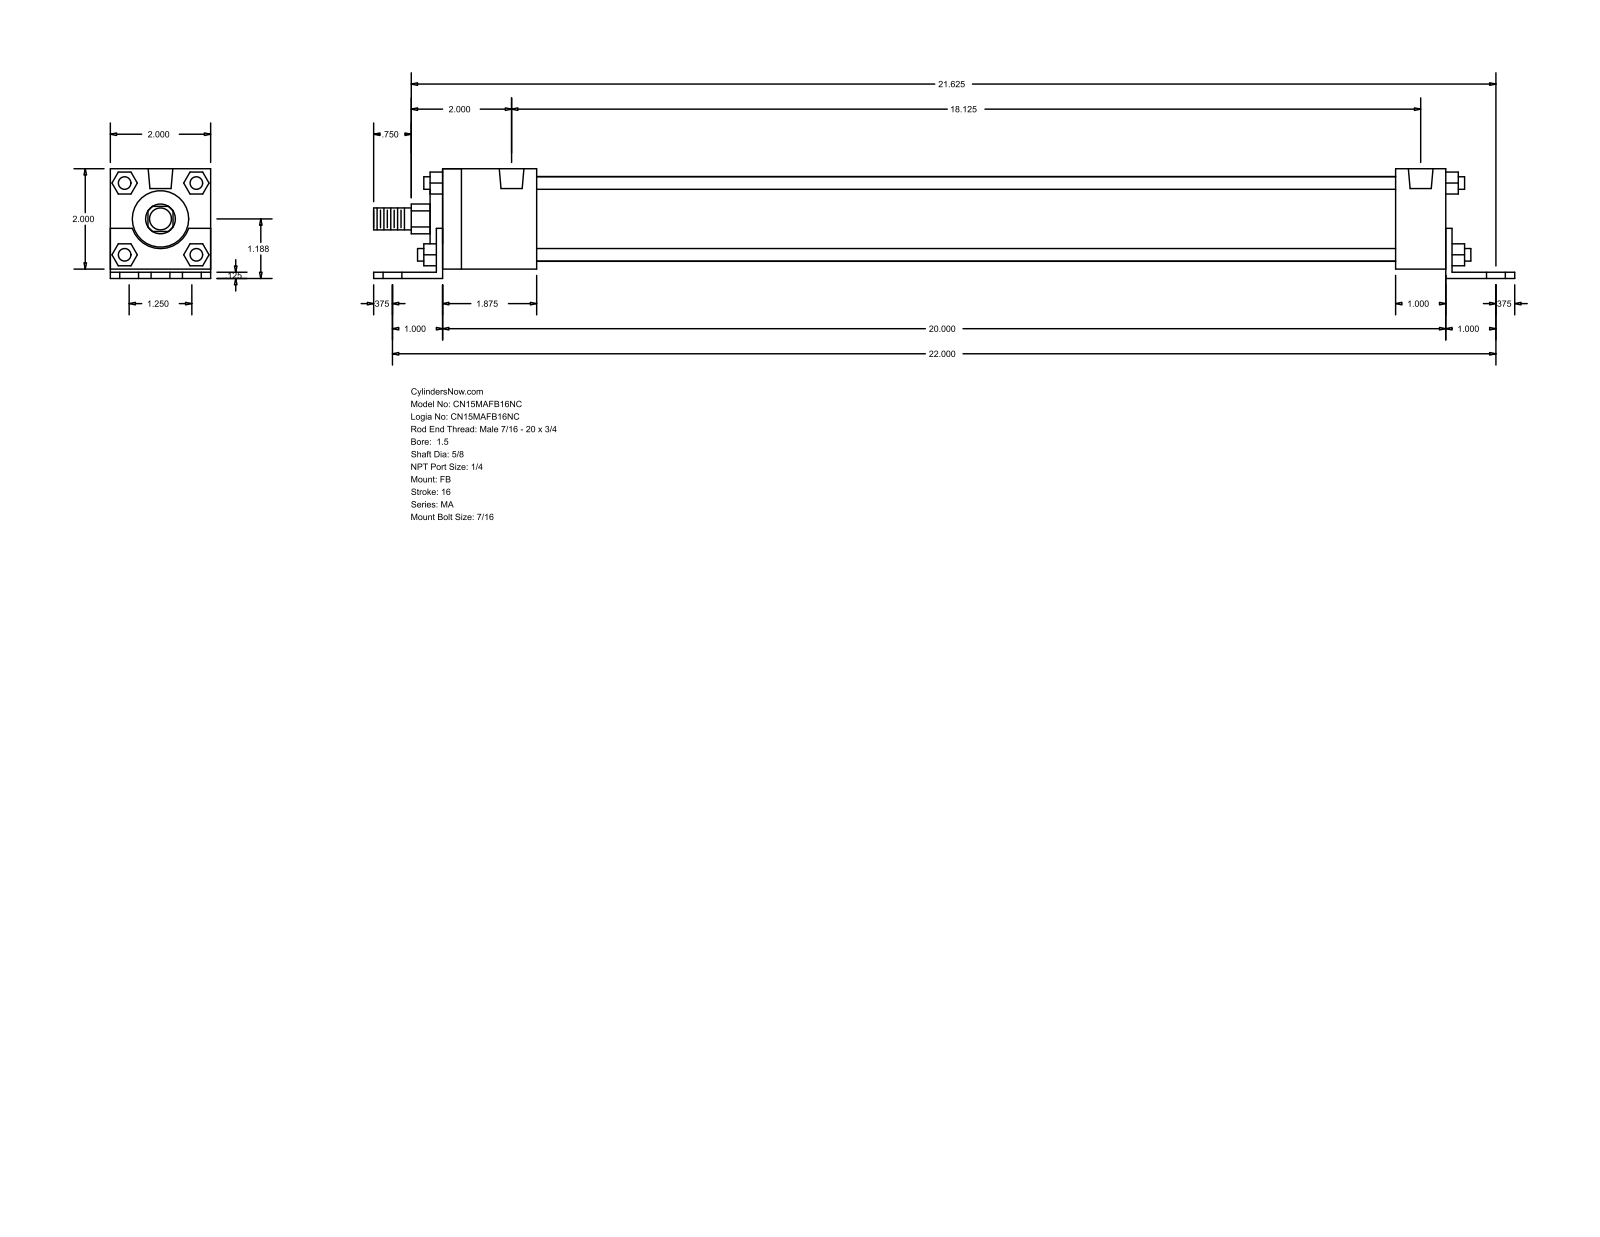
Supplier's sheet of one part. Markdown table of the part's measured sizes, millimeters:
| quantity | value |
| --- | --- |
| part name | MA_FB__0150_0.625 |
| STEP written by | GSSL Pune (CONFIG_CONTROL_DESIGN) |
| units | millimeters |
| bodies | 0 solids, 140 faces (105 planar, 35 cylindrical, 0 other) |
| overall size | 577.85 × 55.56 × 50.8 |
| round holes (diameter × count) | 11.11 × 6, 7.94 × 4, 12.49 × 2 |
| round bosses / shafts (diameter × count) | 6.35 × 4, 42.93 × 1, 28.57 × 1, 15.88 × 1, 11.11 × 1 |
| partial cylindrical surfaces (radius × count) | 7.54 × 1, 15.05 × 1 |
| main face-to-face distances | 50.8, 3.17, 4.76, 55.56, 1.59, 52.39, 25.4, 514.35, 6.35, 3.18 |
| hole center spacings | 15.88, 559.03, 558.8, 31.76, 41.27, 62.38, 460.38, 498.72 |
